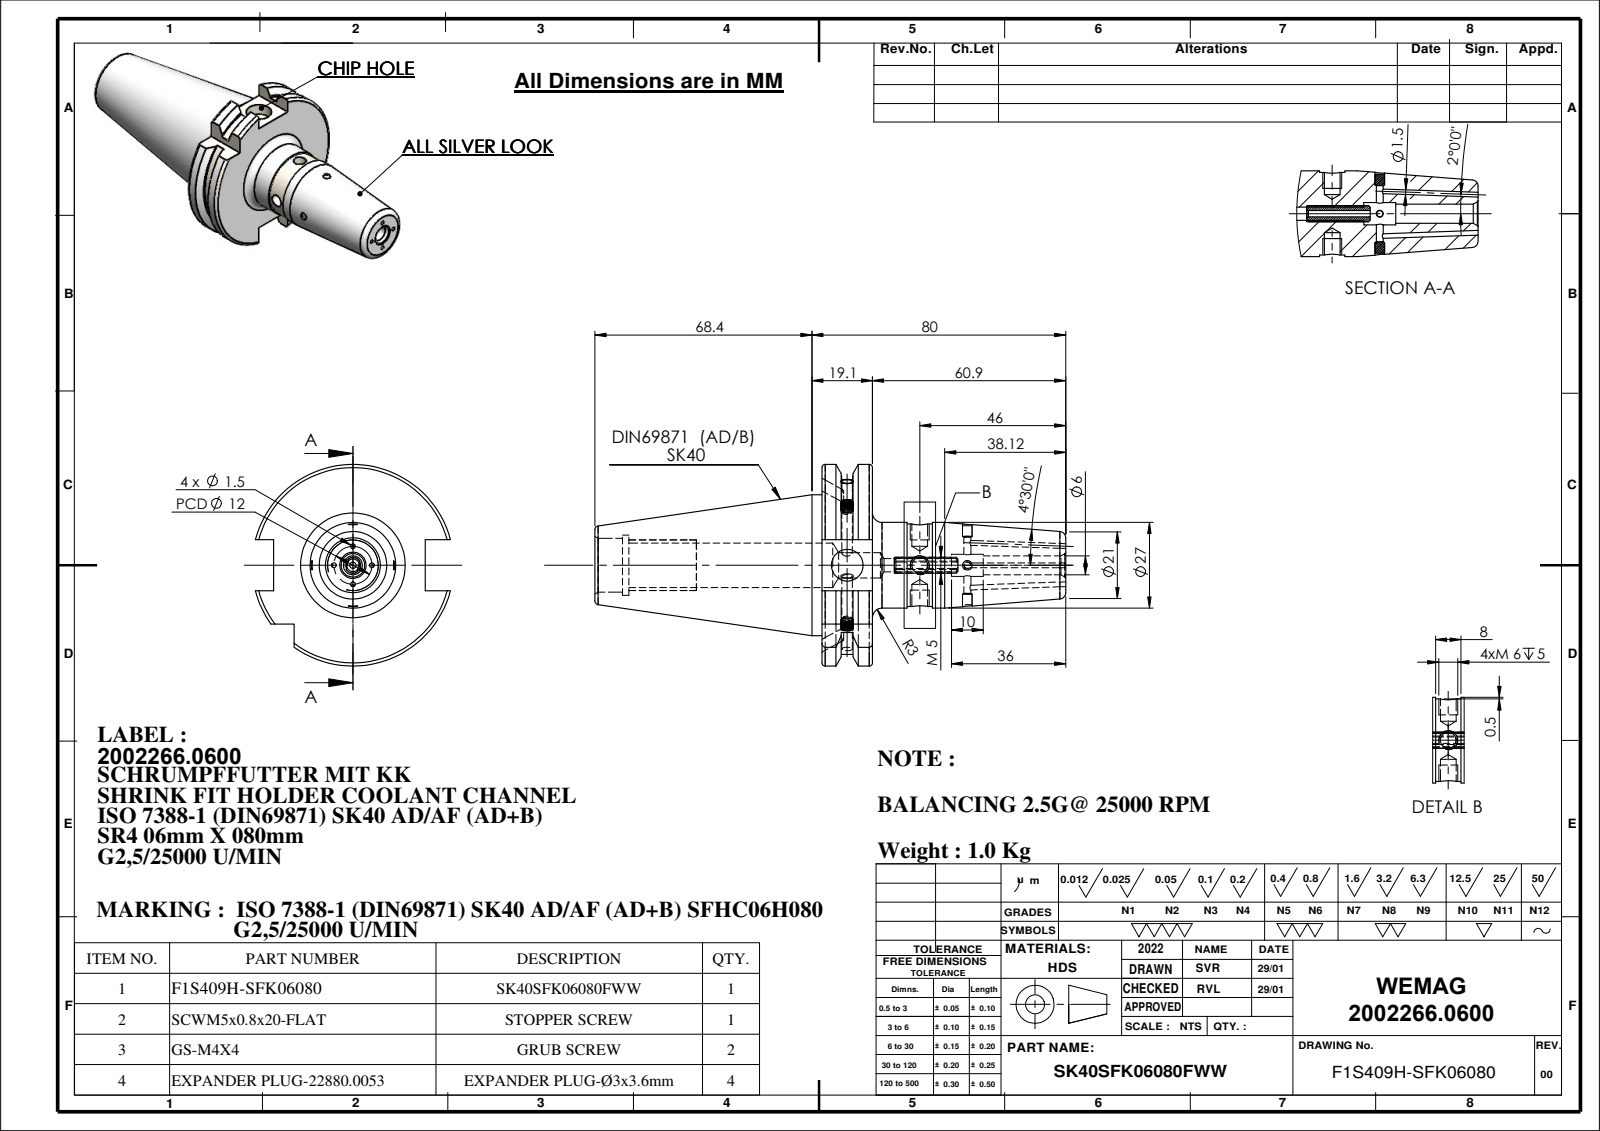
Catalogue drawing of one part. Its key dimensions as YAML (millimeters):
part_name: "EXPANDER PLUG Ø3x3.6; SCWM5x0.8x20-FLAT; SK40SFK06080FWW; 91406-SR406080 (+1 more)"
step_written_by: "SolidWorks 2018 (CONFIG_CONTROL_DESIGN)"
units: millimeters
bodies: {solids: 8, faces: 295, planar: 62, cylindrical: 105, other: 128}
overall_size: [148.4, 63.55, 61.48]
volume: 127479
surface_area: 28985
round_holes:
  - {diameter: 1.5, count: 4}
  - {diameter: 2.2, count: 2}
  - {diameter: 3, count: 2}
  - {diameter: 5, count: 2}
  - {diameter: 2, count: 1}
  - {diameter: 3.3, count: 1}
  - {diameter: 4.2, count: 1}
  - {diameter: 5.99, count: 1}
  - {diameter: 6.99, count: 1}
  - {diameter: 8, count: 1}
  - {diameter: 10, count: 1}
  - {diameter: 14, count: 1}
round_bosses_or_shafts:
  - {diameter: 4, count: 2}
  - {diameter: 44.45, count: 1}
  - {diameter: 27, count: 1}
  - {diameter: 26, count: 1}
partial_cylinders:
  - {radius: 2.5, count: 1}
  - {radius: 28.12, count: 1}
  - {radius: 31.77, count: 1}
face_to_face_distances: [15.9, 60.9, 76.8, 16.1, 47.8, 3.5, 71.6, 87.5, 148.4, 10.7]
hole_center_spacings: [15, 22.85, 37.85]
